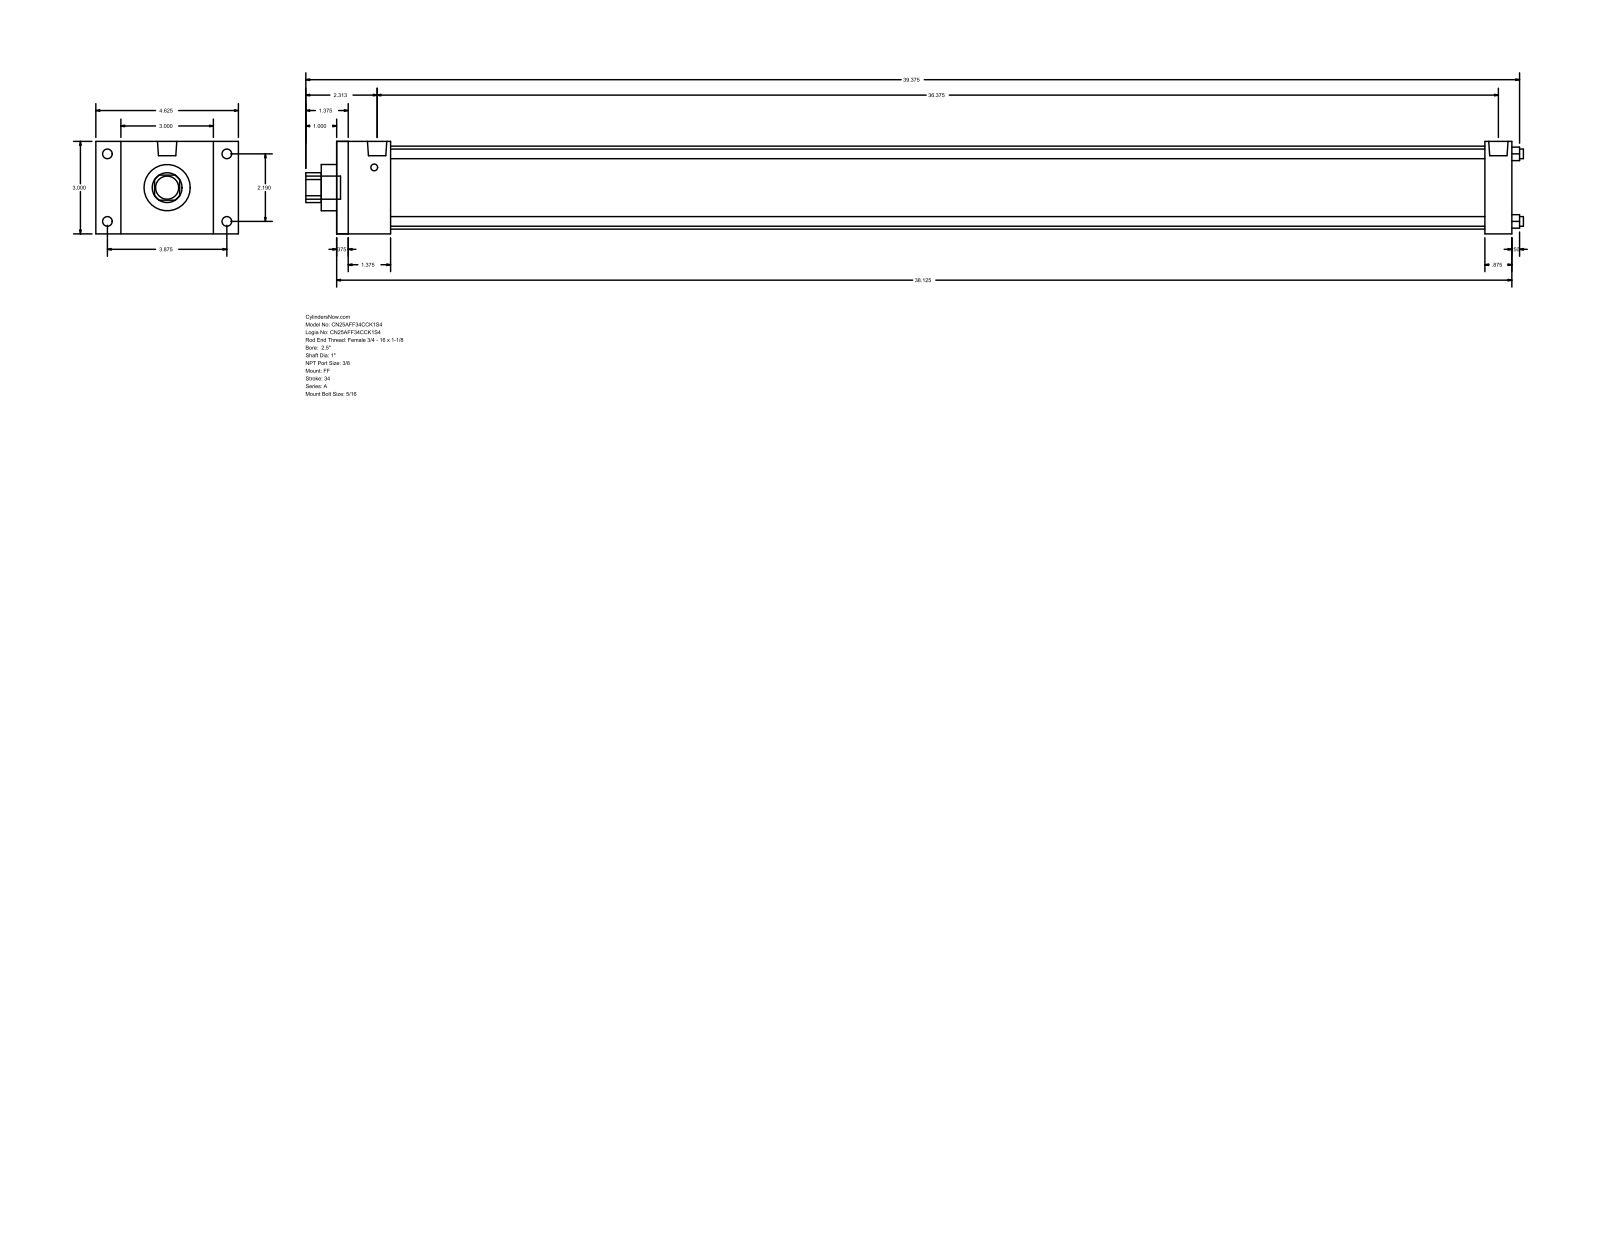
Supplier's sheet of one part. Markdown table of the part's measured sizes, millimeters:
| quantity | value |
| --- | --- |
| part name | A_FF__0250_1 |
| STEP written by | GSSL Pune (CONFIG_CONTROL_DESIGN) |
| units | millimeters |
| bodies | 0 solids, 92 faces (64 planar, 28 cylindrical, 0 other) |
| overall size | 1003.3 × 117.47 × 76.2 |
| round holes (diameter × count) | 7.94 × 4, 25.4 × 1, 38.1 × 1, 68.33 × 1 |
| round bosses / shafts (diameter × count) | 7.94 × 4, 5.56 × 4, 15.93 × 2, 19.05 × 1 |
| partial cylindrical surfaces (radius × count) | 12.29 × 1 |
| main face-to-face distances | 76.2, 968.37, 958.85, 9.52, 22.22, 44.45, 946.15, 34.93, 936.63, 901.7 |
| hole center spacings | 39.33, 55.62, 78.66 |
